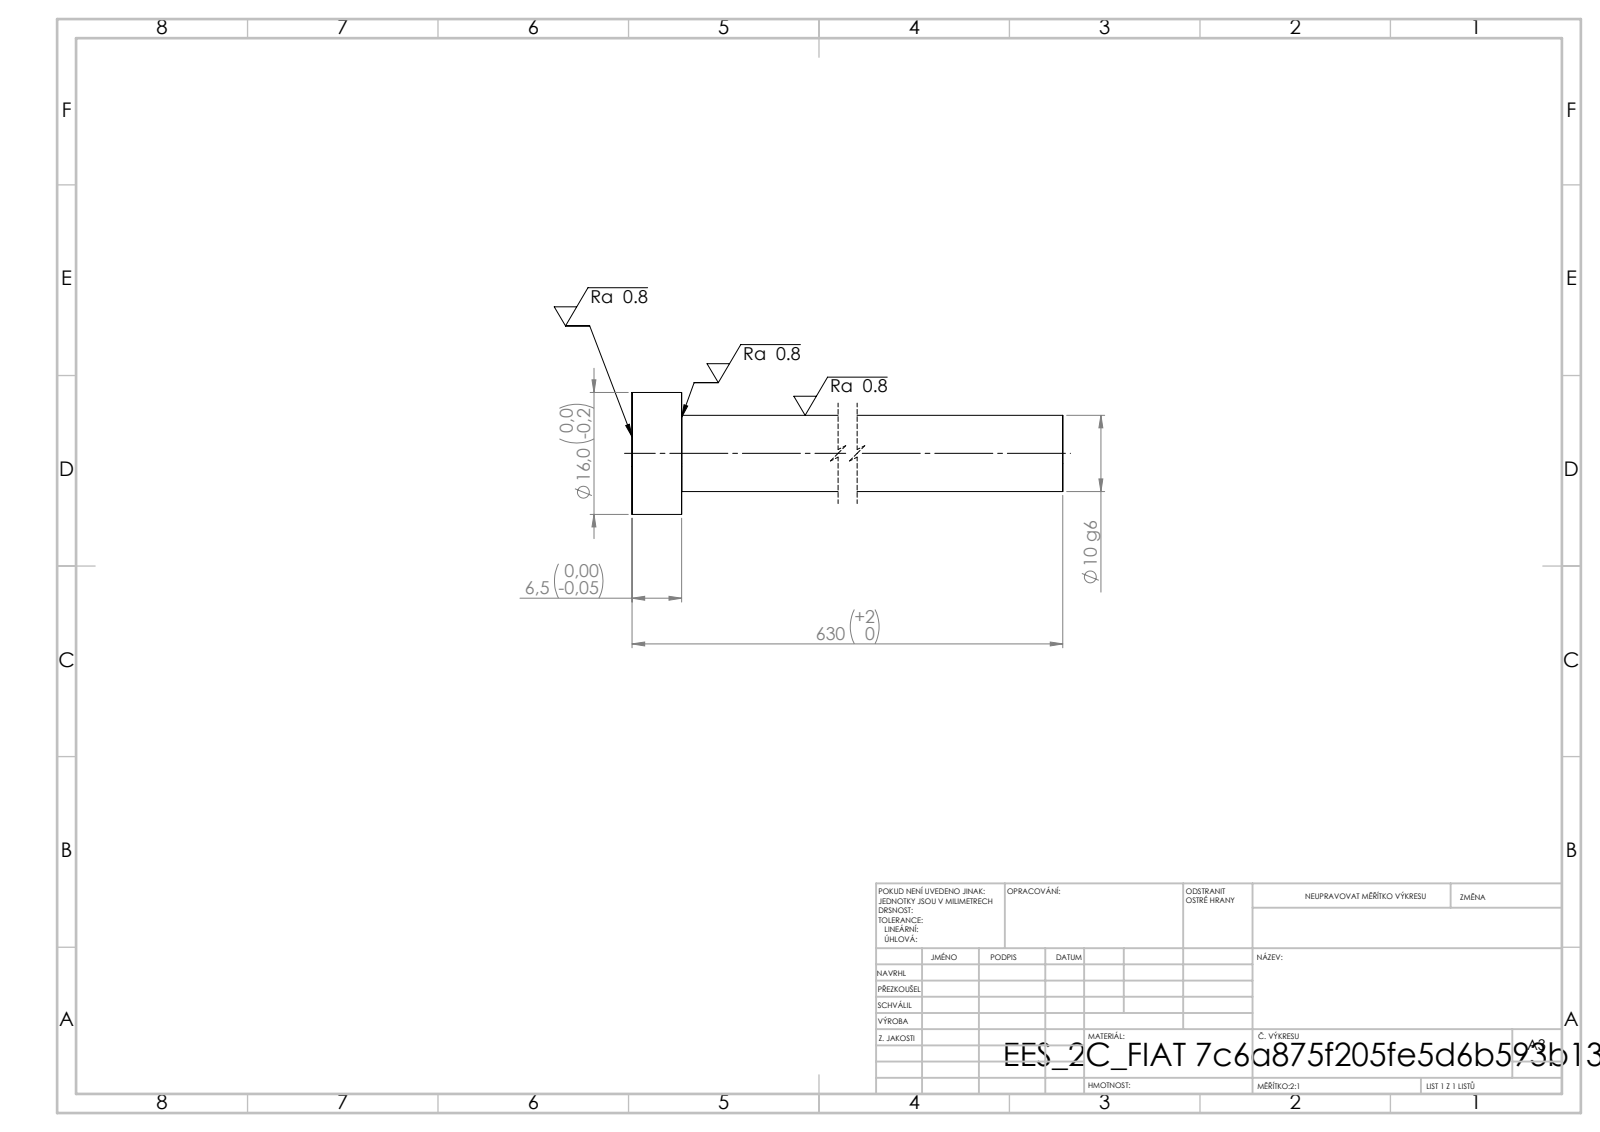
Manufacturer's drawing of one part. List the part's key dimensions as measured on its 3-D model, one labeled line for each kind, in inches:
STEP written by: SolidWorks 2019 (CONFIG_CONTROL_DESIGN)
Units: inches
Bodies: 1 solid, 7 faces (3 planar, 4 cylindrical, 0 other)
Overall size (bounding box): 24.803 × 0.63 × 0.63
Volume: 3.068 in³ · Surface area: 31.49 in²
Round bosses / shafts (diameter × count): ⌀0.63 ×1, ⌀0.394 ×1
Main face-to-face distances: 0.256, 24.803, 24.547
